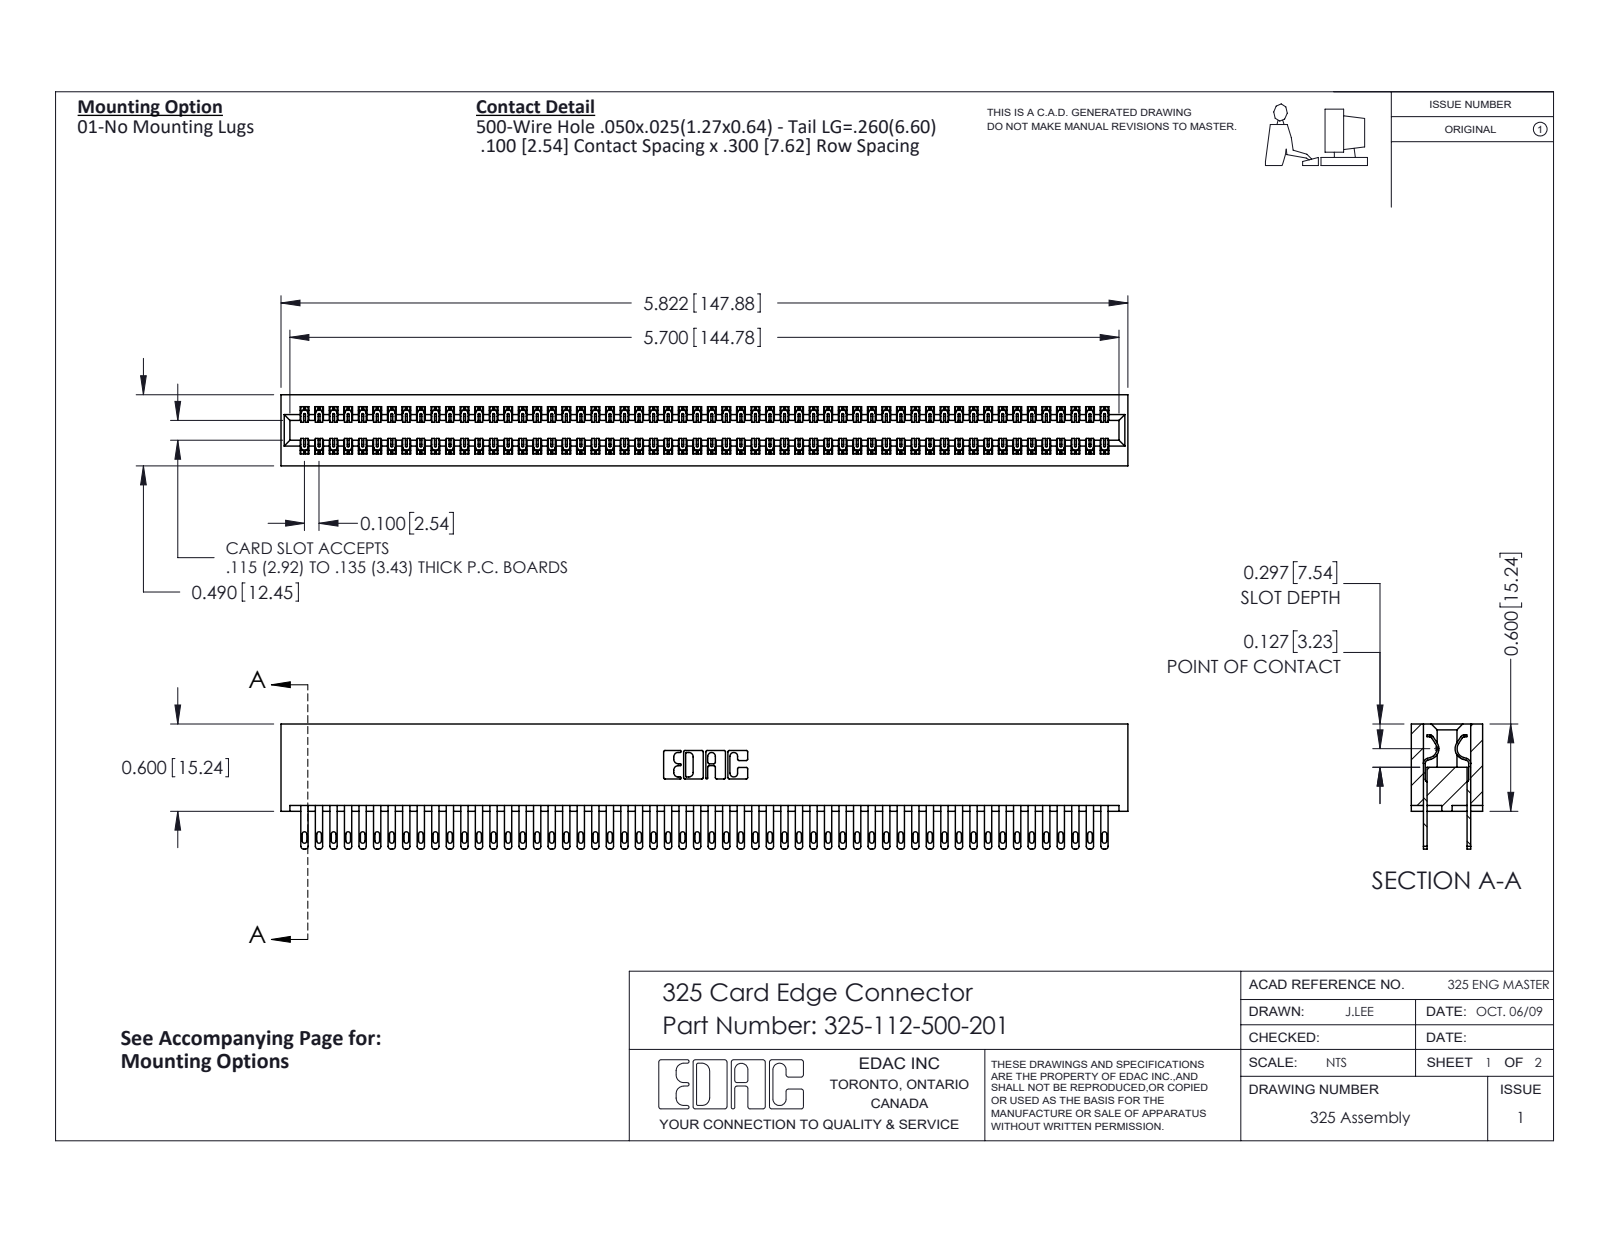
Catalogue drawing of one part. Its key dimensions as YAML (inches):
part_name: "325-112-500-201; 325 Part_Lugless; 325-292-001_325-293-100"
step_written_by: "SolidWorks 2016 (CONFIG_CONTROL_DESIGN)"
units: inches
bodies: {solids: 113, faces: 5482, planar: 3426, cylindrical: 2056, other: 0}
overall_size: [5.822, 0.86, 0.49]
volume: 1.231
surface_area: 41.18
partial_cylinders:
  - {radius: 0.006, count: 168}
  - {radius: 0.016, count: 112}
  - {radius: 0.02, count: 112}
  - {radius: 0.01, count: 22}
  - {radius: 0.007, count: 6}
  - {radius: 0.031, count: 6}
  - {radius: 0.026, count: 3}
  - {radius: 0.014, count: 2}
face_to_face_distances: [0.083, 0.407, 0.3, 0.107, 0.383, 0.025, 0.325, 0.49, 0.275, 0.263]
